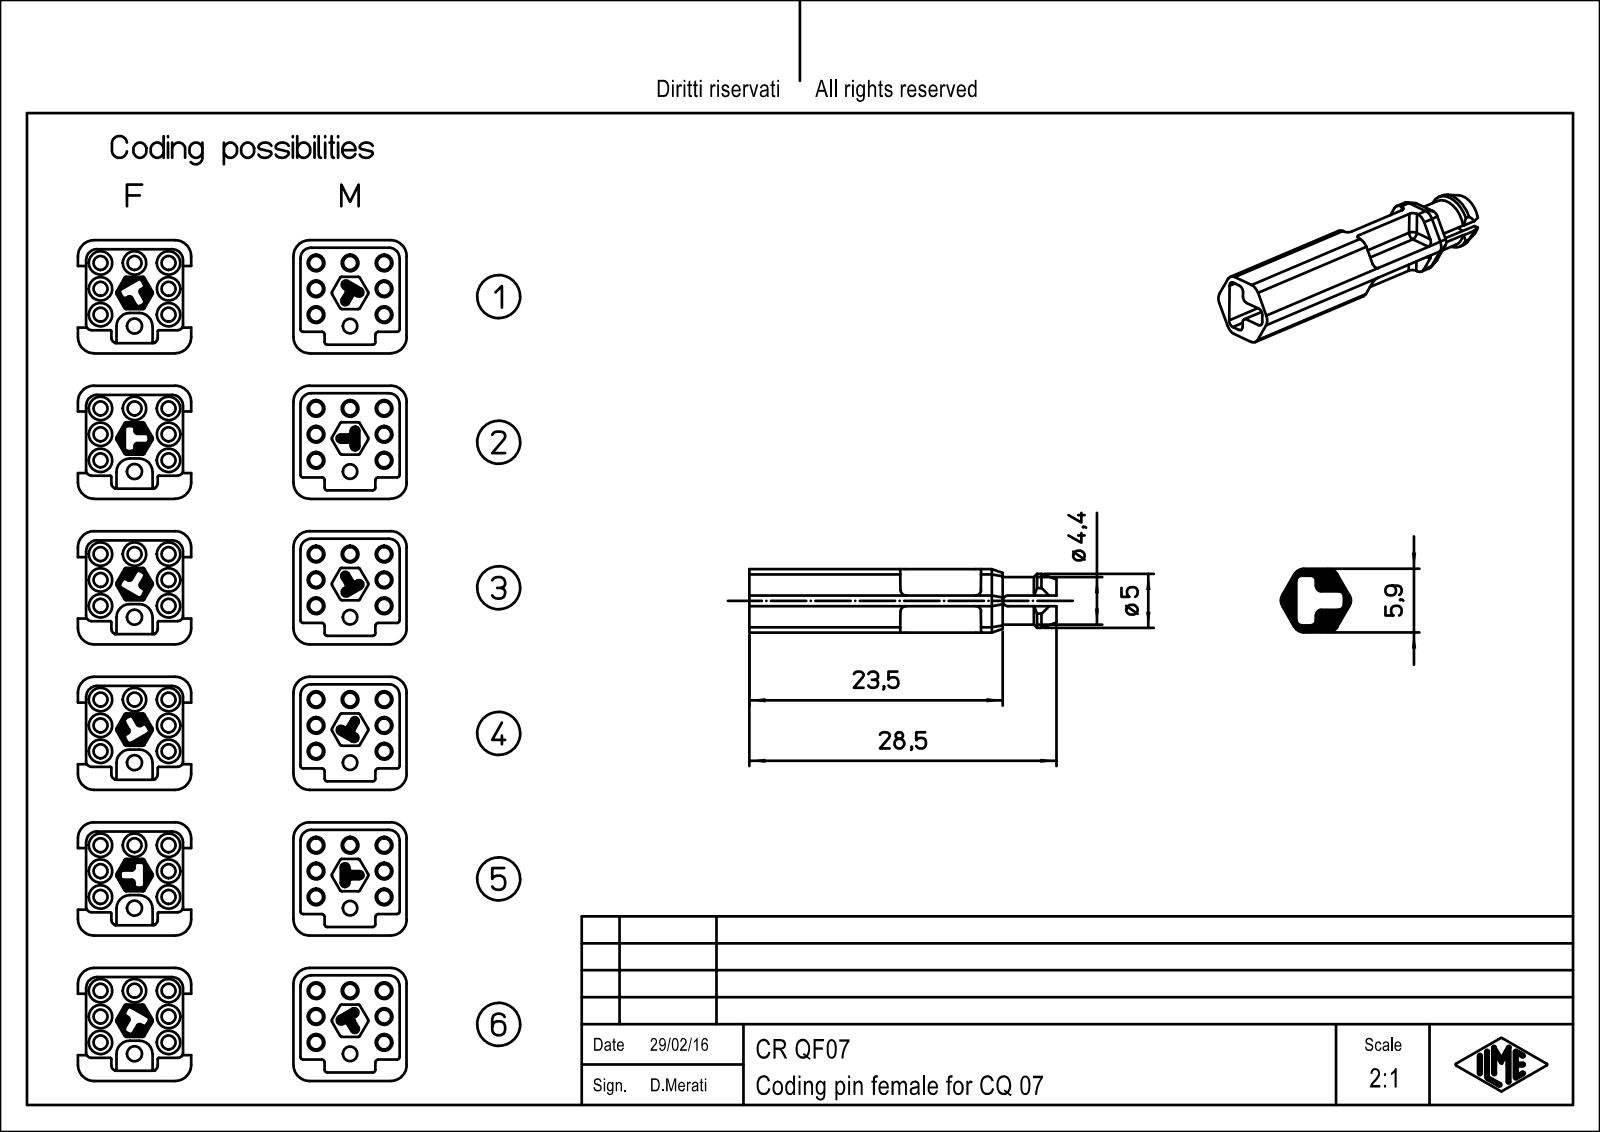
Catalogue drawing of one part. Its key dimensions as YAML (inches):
part_name: "CR_QF07"
step_written_by: "PTC Creo Elements/Direct Modeling 19.0B 21-Mar-2015 (C) Parametric Technology GmbH (AUTOMOTIVE_DESIGN)"
units: inches
bodies: {solids: 1, faces: 24, planar: 18, cylindrical: 4, other: 2}
overall_size: [1.122, 0.268, 0.232]
volume: 0.038
surface_area: 1.32
round_bosses_or_shafts:
  - {diameter: 0.197, count: 1}
  - {diameter: 0.173, count: 1}
face_to_face_distances: [0.232, 0.083, 0.15, 0.026, 0.207, 0.057, 0.124, 0.071, 0.067, 0.181]
